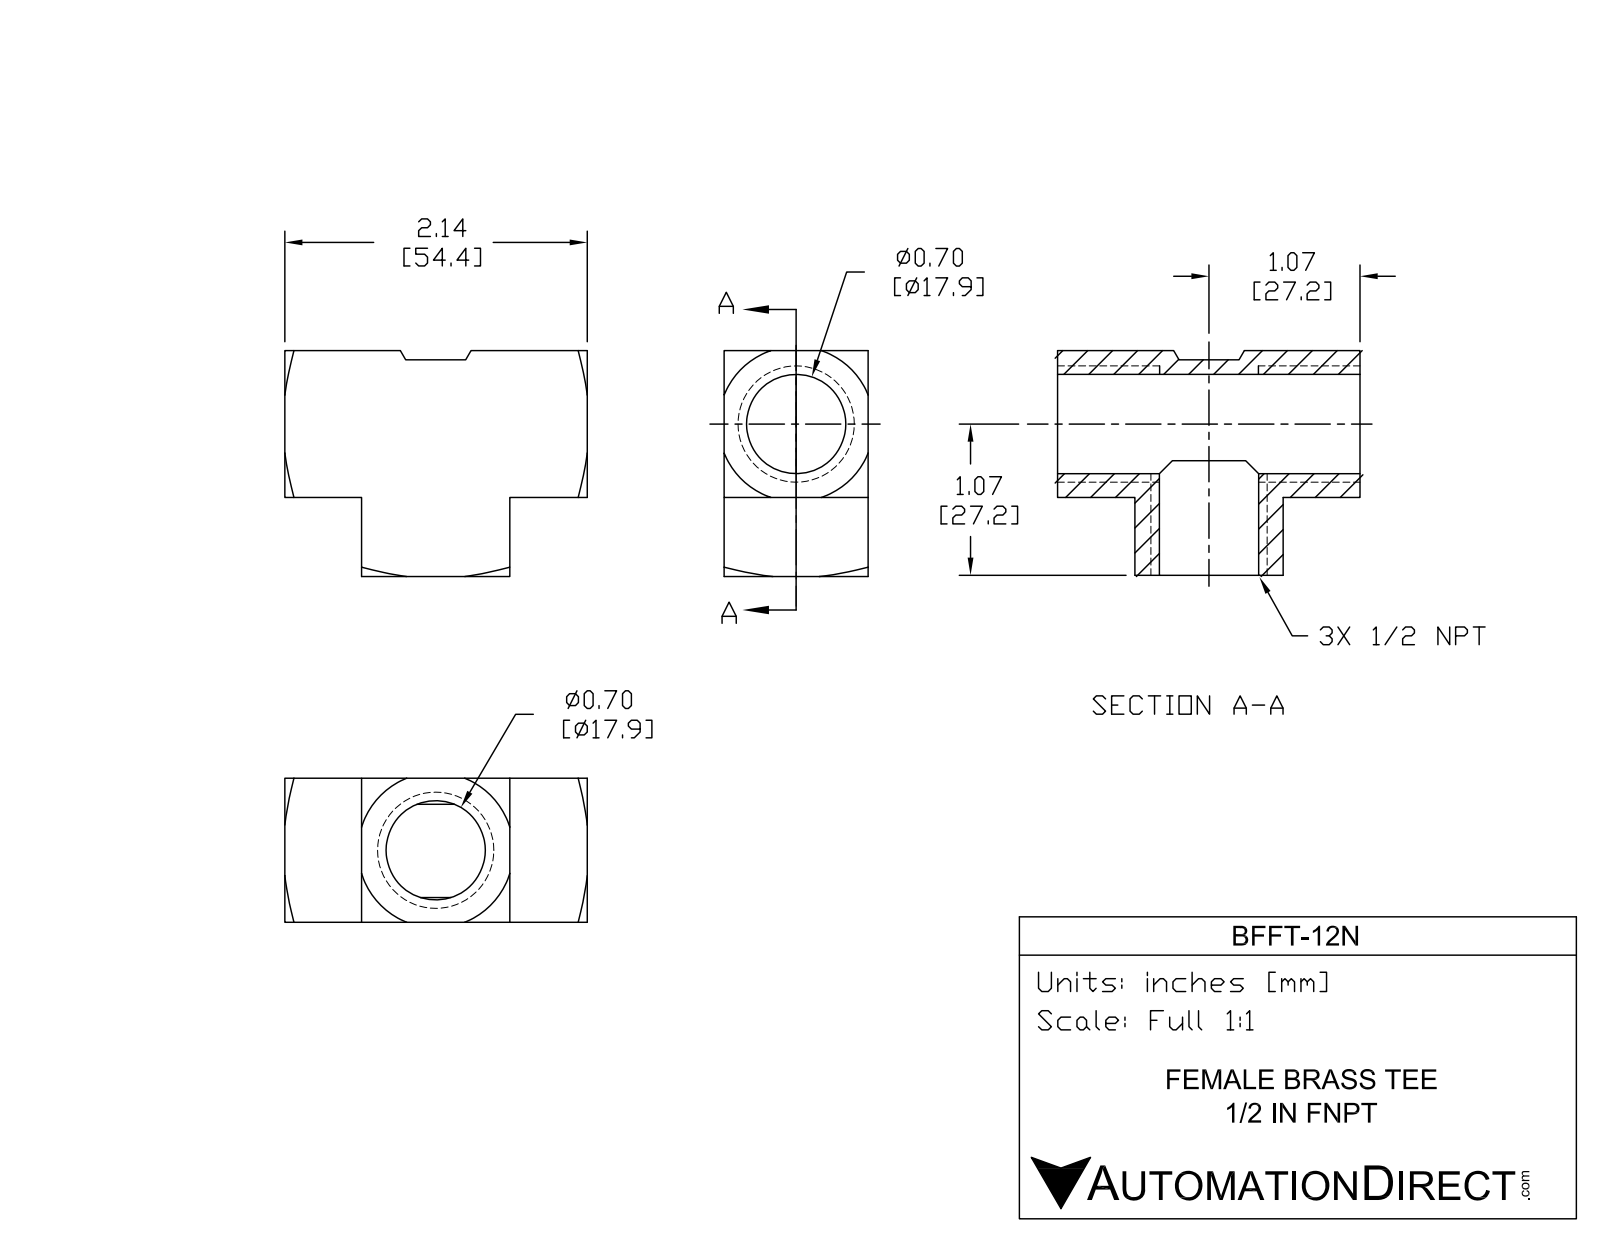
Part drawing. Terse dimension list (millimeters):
name: BFFT-12N
written by: SolidWorks 2015 (CONFIG_CONTROL_DESIGN)
unit: mm
bodies: 1 solid, 36 faces (16 planar, 8 cylindrical, 12 other)
size: 54.4 × 40.6 × 25.9
volume: 27 790 mm³; area: 11 630 mm²
holes: 2× ⌀17.9
face distances: 25.9, 26.4, 26.7, 40.6, 14.2, 14.4, 41, 54.4, 40, 13.3
